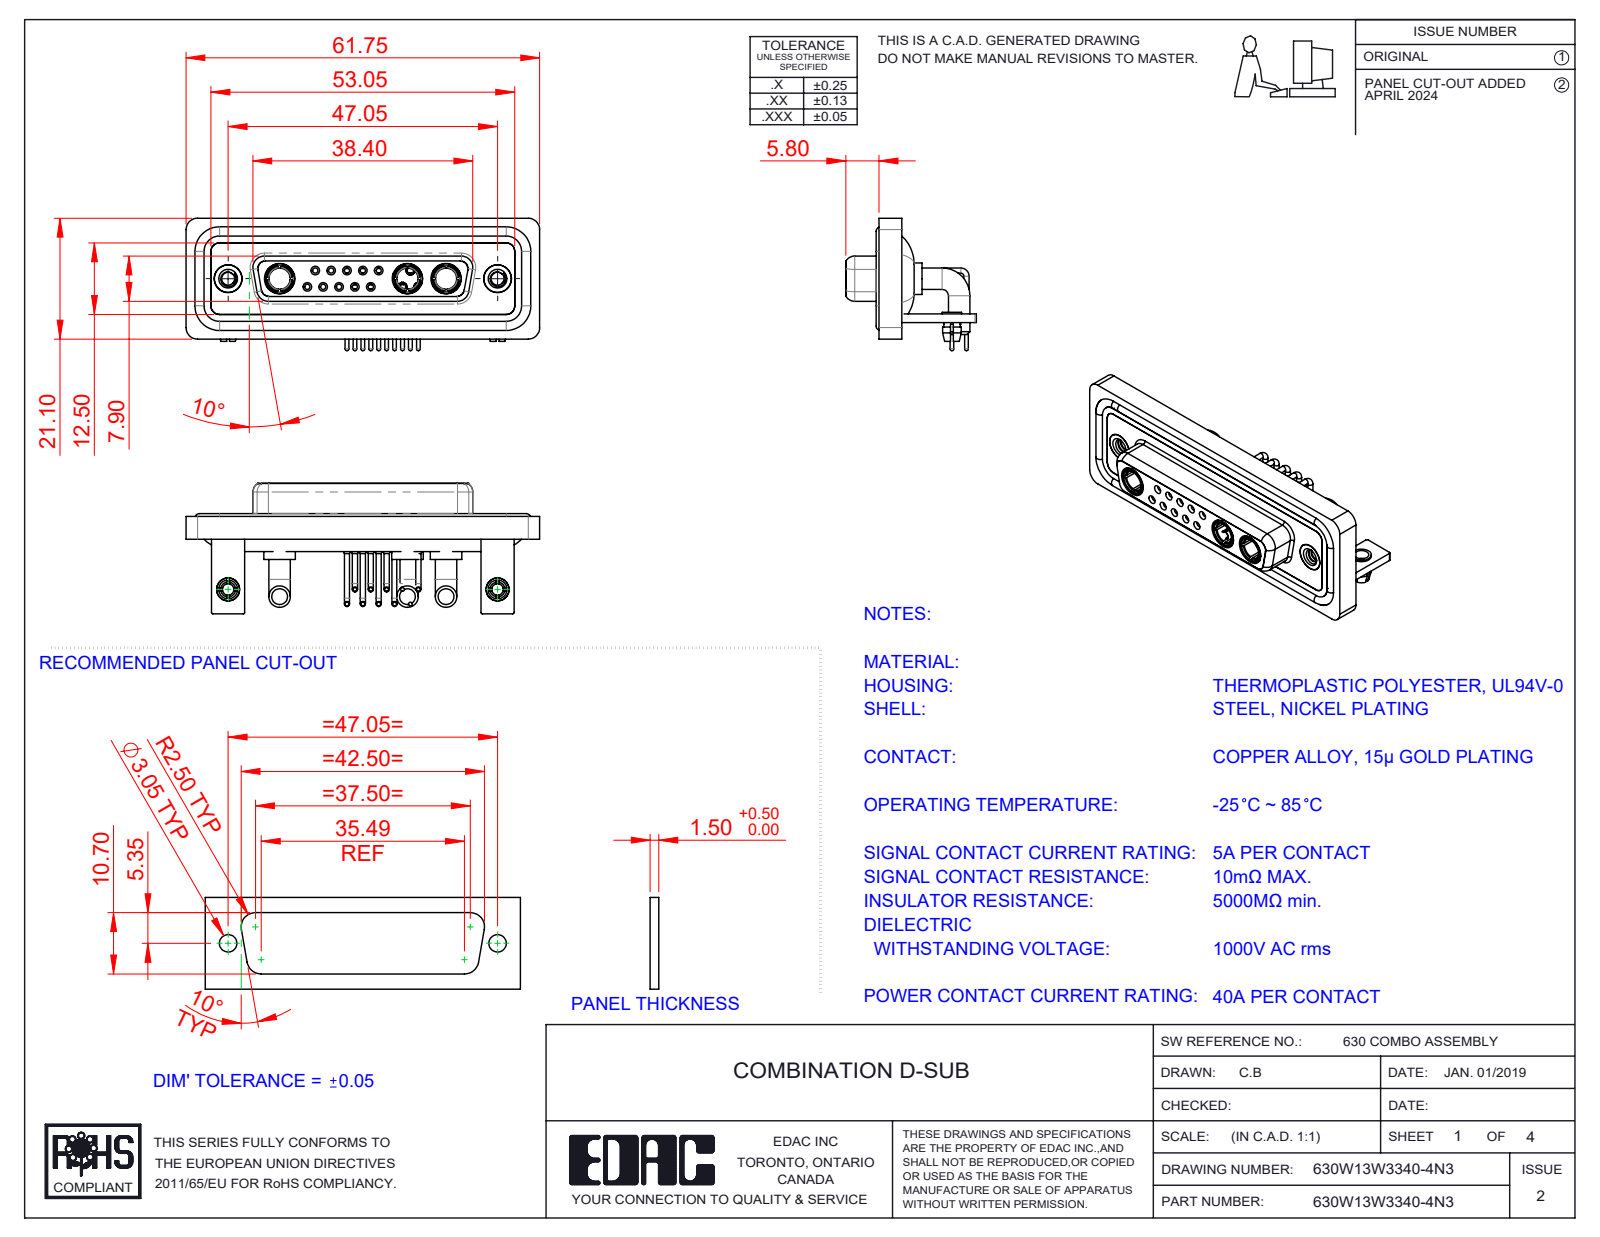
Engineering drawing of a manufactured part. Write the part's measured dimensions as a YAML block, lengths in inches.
part_name: "630Combo Shell Front_25 Contacts; 630Combo Waterproof Housing_25 Contacts; 630Combo Shell Rear_25 Contacts; 630Combo Stabilizer Bracket_50 Contacts (+7 more)"
step_written_by: "SolidWorks 2023 (CONFIG_CONTROL_DESIGN)"
units: inches
bodies: {solids: 27, faces: 1290, planar: 410, cylindrical: 549, other: 331}
overall_size: [2.431, 0.91, 0.898]
volume: 0.555
surface_area: 23.83
round_holes:
  - {diameter: 0.079, count: 12}
  - {diameter: 0.035, count: 10}
  - {diameter: 0.043, count: 10}
  - {diameter: 0.059, count: 10}
  - {diameter: 0.063, count: 5}
  - {diameter: 0.067, count: 5}
  - {diameter: 0.191, count: 5}
  - {diameter: 0.146, count: 3}
  - {diameter: 0.209, count: 3}
  - {diameter: 0.089, count: 2}
  - {diameter: 0.098, count: 2}
  - {diameter: 0.126, count: 2}
round_bosses_or_shafts:
  - {diameter: 0.035, count: 15}
  - {diameter: 0.063, count: 12}
  - {diameter: 0.026, count: 10}
  - {diameter: 0.148, count: 6}
  - {diameter: 0.079, count: 5}
  - {diameter: 0.059, count: 5}
  - {diameter: 0.217, count: 3}
  - {diameter: 0.205, count: 3}
partial_cylinders:
  - {radius: 0.079, count: 19}
  - {radius: 0.059, count: 18}
  - {radius: 0.01, count: 16}
  - {radius: 0.053, count: 8}
  - {radius: 0.063, count: 8}
  - {radius: 0.02, count: 5}
  - {radius: 0.024, count: 4}
  - {radius: 0.026, count: 4}
face_to_face_distances: [0.016, 0.071, 0.114, 0.146, 0.059, 0.161, 0.043, 0.055, 0.063, 0.122]
hole_center_spacings: [0.124, 0.109, 0.218, 0.198, 0.327, 0.198, 0.295, 0.436]
